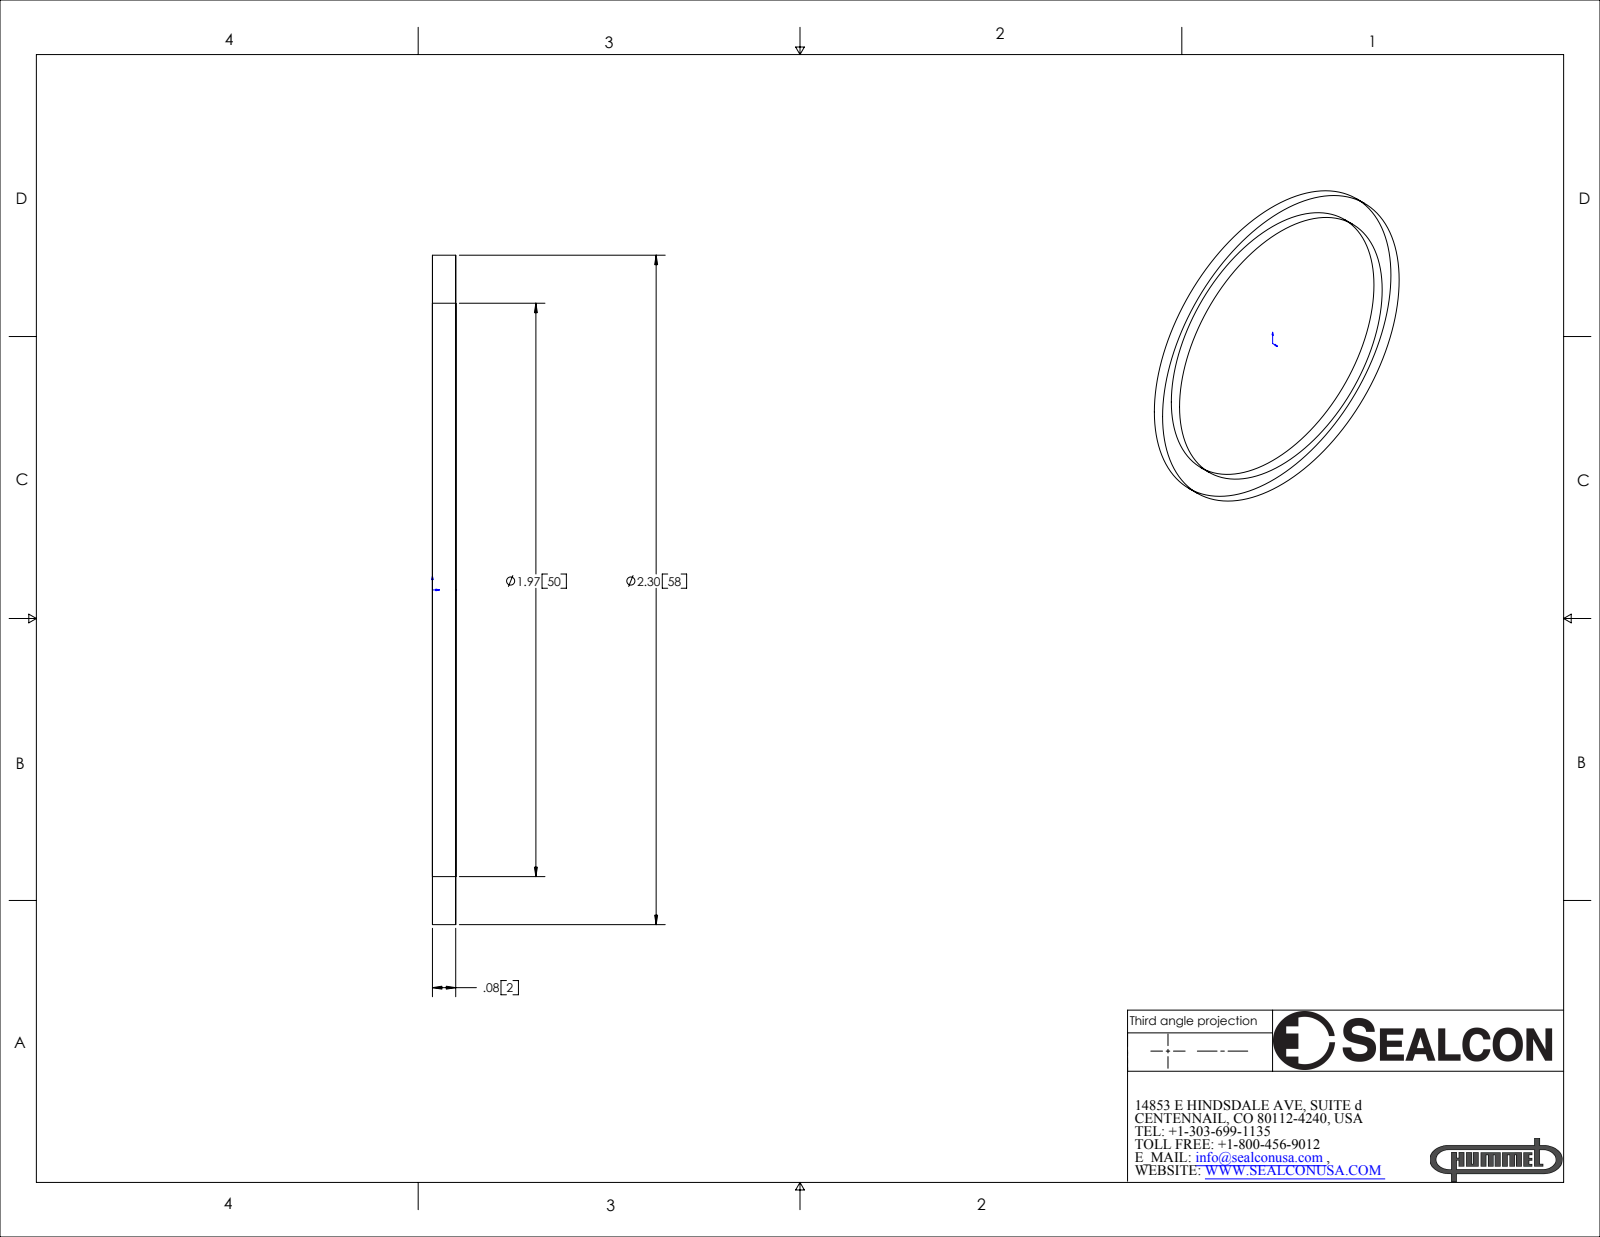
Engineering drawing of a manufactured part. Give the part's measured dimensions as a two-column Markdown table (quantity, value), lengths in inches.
| quantity | value |
| --- | --- |
| part name | MS-50-NY |
| STEP written by | SolidWorks 2007 (CONFIG_CONTROL_DESIGN) |
| units | inches |
| bodies | 1 solid, 6 faces (2 planar, 4 cylindrical, 0 other) |
| overall size | 2.3 × 2.3 × 0.08 |
| volume | 0.089 in³ |
| surface area | 3.287 in² |
| round holes (diameter × count) | 1.97 × 1 |
| round bosses / shafts (diameter × count) | 2.3 × 1 |
| main face-to-face distances | 0.08 |
